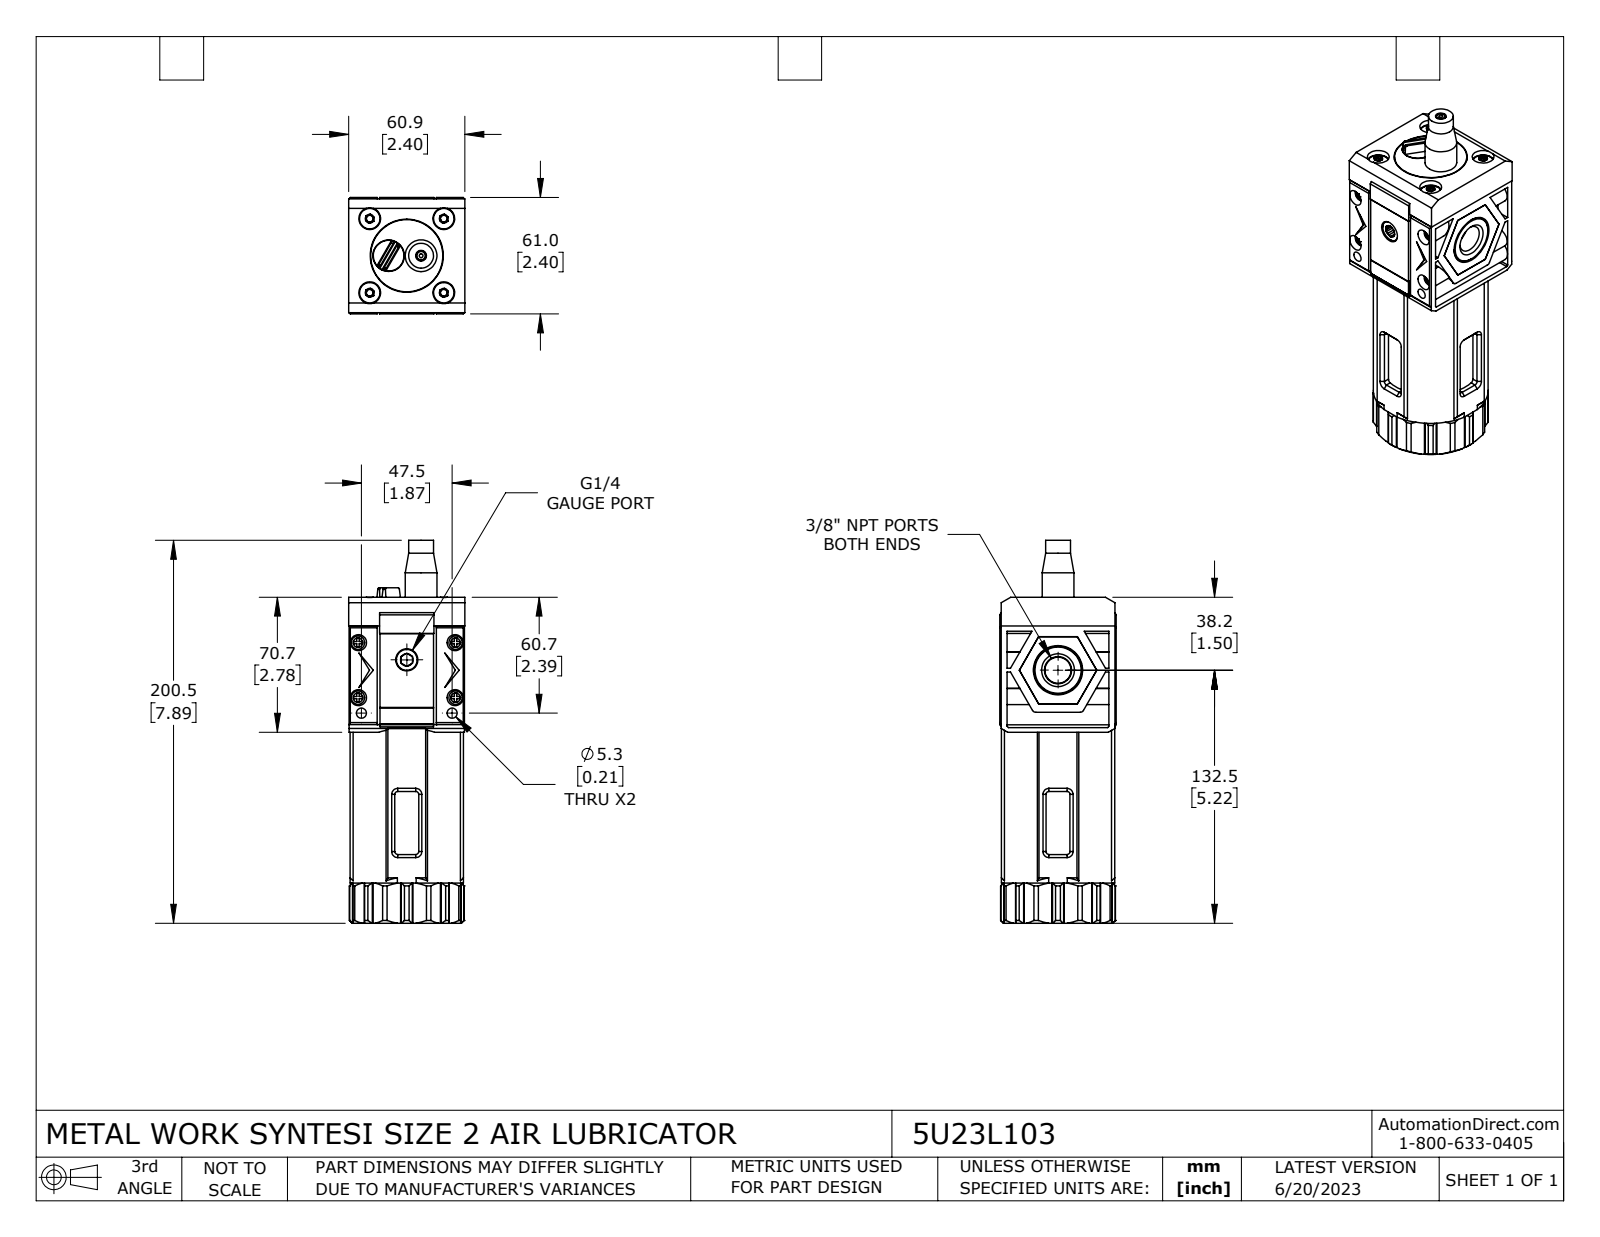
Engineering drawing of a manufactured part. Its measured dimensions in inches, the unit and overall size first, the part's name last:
Units: inches
Overall size (bounding box): 7.894 × 2.402 × 2.398
Round holes (diameter × count): ⌀0.128 ×4, ⌀0.165 ×4, ⌀0.331 ×4, ⌀0.449 ×4, ⌀0.209 ×2, ⌀0.22 ×1, ⌀0.457 ×1, ⌀0.65 ×1, ⌀1.25 ×1, ⌀1.508 ×1, ⌀1.929 ×1, ⌀1.969 ×1
Round bosses / shafts (diameter × count): ⌀0.276 ×4, ⌀0.189 ×4, ⌀0.15 ×4, ⌀1.488 ×1, ⌀1.248 ×1, ⌀1.035 ×1, ⌀0.925 ×1, ⌀0.917 ×1
Partial cylindrical surfaces — rounded edges, fillets, slot ends (radius × count): R0.011 ×28, R0.02 ×16, R0.059 ×8, R0.069 ×4, R0.191 ×4, R0.008 ×2, R0.079 ×2, R0.242 ×2
Main face-to-face distances: 2.39, 5.303, 3.205, 2.098, 1.13, 2.193, 2.402, 0.031, 3.11, 0.094
Hole centre spacings: 1.08, 1.528, 0.325, 0.857, 0.896, 1.057, 1.134, 1.265
Volume: 23.53 in³ · Surface area: 189.8 in²
Bodies: 14 solids, 1060 faces (531 planar, 318 cylindrical, 211 other)
Part name (STEP PRODUCT): 5U23L103
STEP written by: SolidWorks 2021 (CONFIG_CONTROL_DESIGN)
